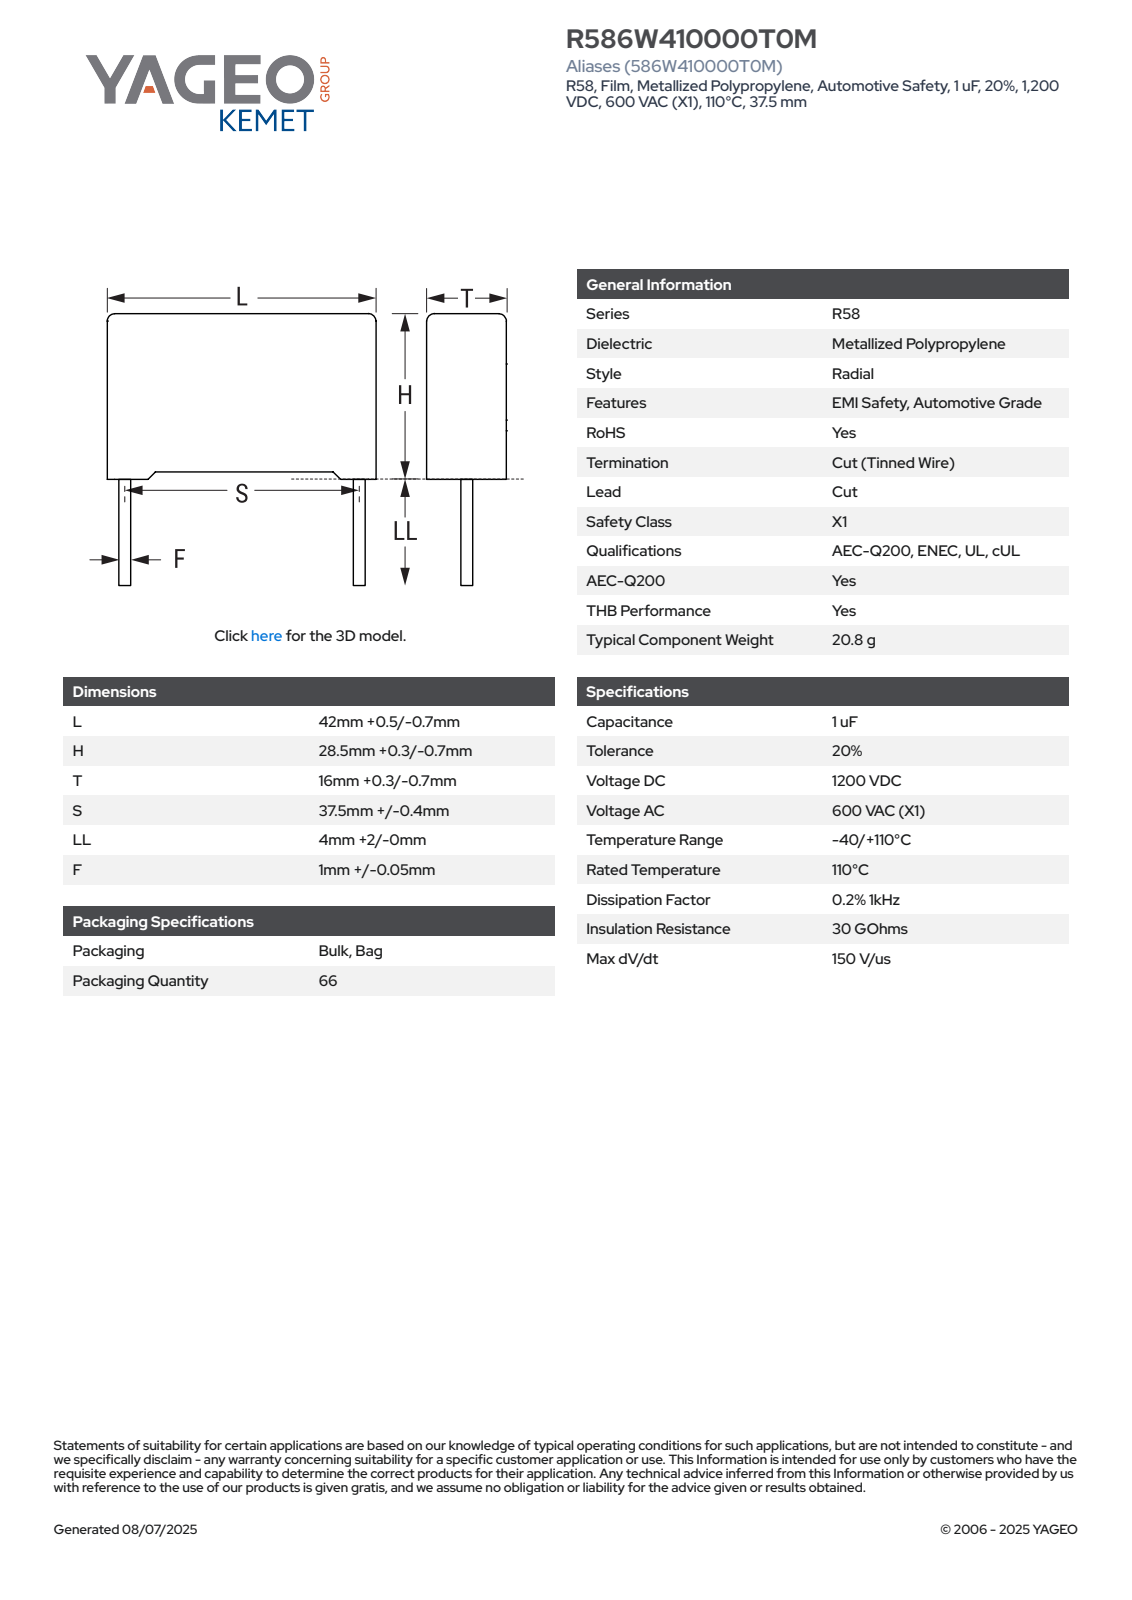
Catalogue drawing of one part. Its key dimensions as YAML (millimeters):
part_name: "CFR_RB2_42X28.5X16_L42.5H28.8T16.3S37.5LL6F1.05"
step_written_by: "SolidWorks 2021 (AUTOMOTIVE_DESIGN)"
units: millimeters
bodies: {solids: 4, faces: 85, planar: 77, cylindrical: 8, other: 0}
overall_size: [42.5, 34.8, 16.3]
volume: 19356
surface_area: 4894
round_bosses_or_shafts:
  - {diameter: 1.05, count: 2}
partial_cylinders:
  - {radius: 0.5, count: 4}
face_to_face_distances: [16.3, 27.81, 42.5, 28.05, 0.75, 0.99, 28.8, 16.31, 1.42, 41.08]
